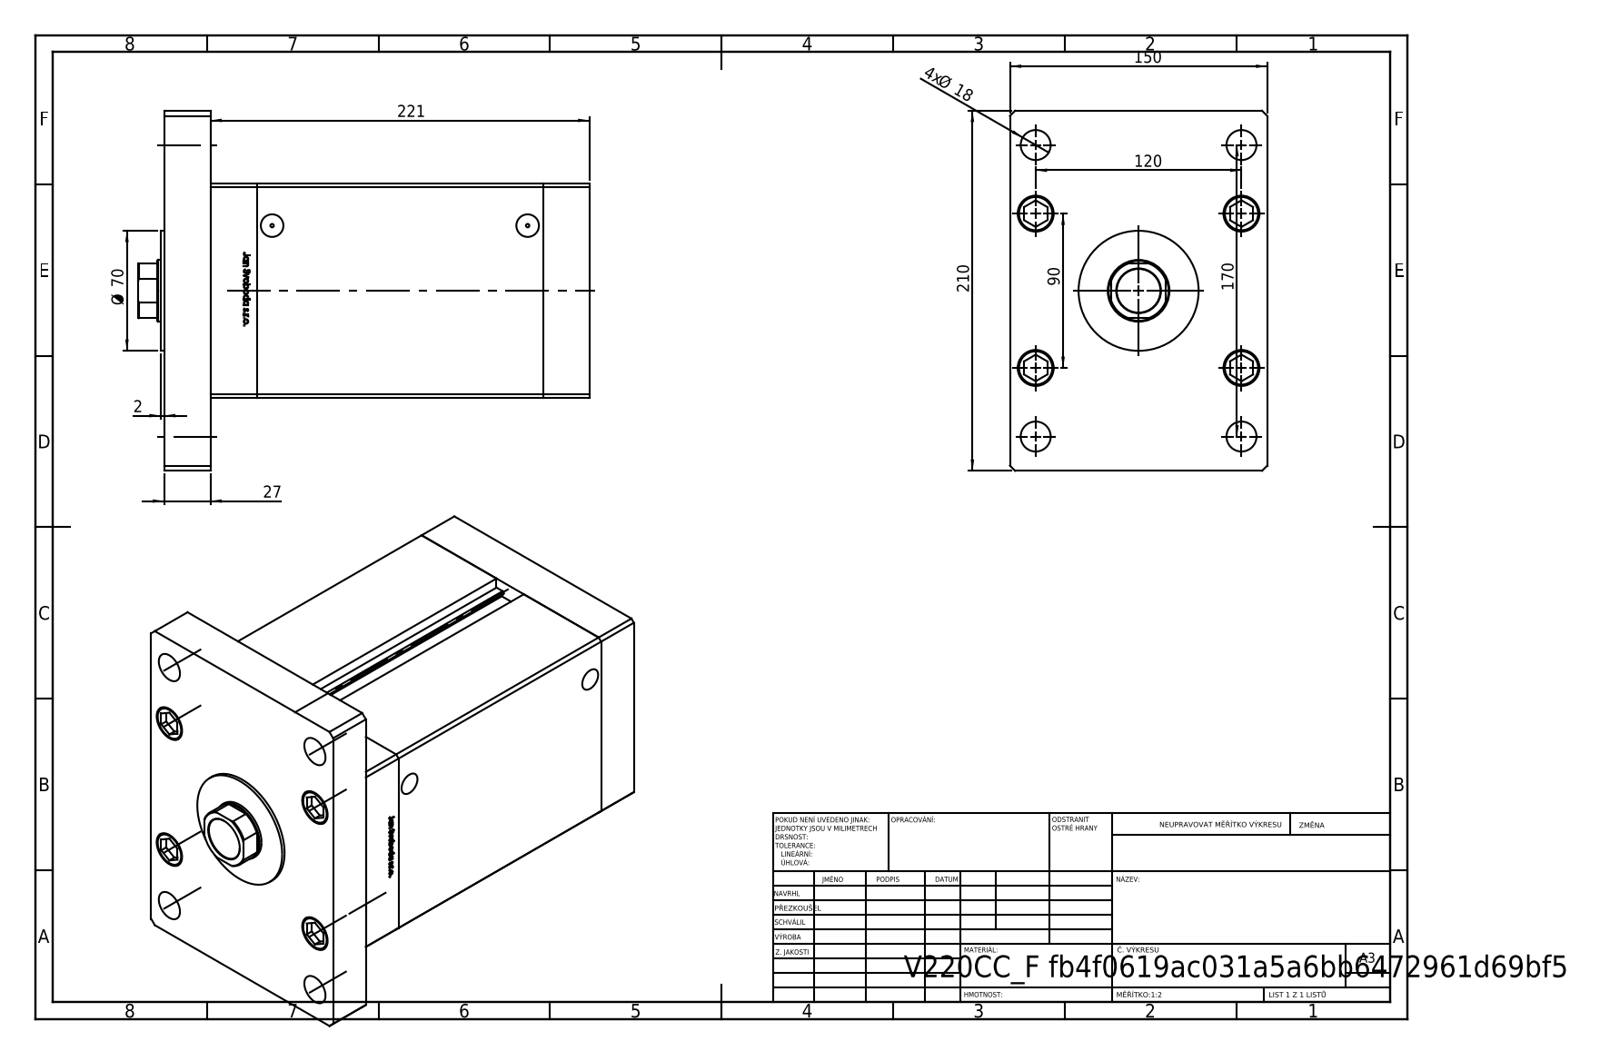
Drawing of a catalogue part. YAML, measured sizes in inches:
part_name: "ALLEN BOLT; V220C_FRONT_F; V220C_VC_F; V220C_F (+2 more)"
step_written_by: "SolidWorks 2019 (CONFIG_CONTROL_DESIGN)"
units: inches
bodies: {solids: 19, faces: 1308, planar: 515, cylindrical: 187, other: 606}
overall_size: [10.354, 8.268, 5.906]
volume: 266.2
surface_area: 731.9
round_holes:
  - {diameter: 0.689, count: 9}
  - {diameter: 0.866, count: 5}
  - {diameter: 0.63, count: 4}
  - {diameter: 0.827, count: 4}
  - {diameter: 0.079, count: 2}
  - {diameter: 0.518, count: 2}
  - {diameter: 1.004, count: 1}
  - {diameter: 1.417, count: 1}
  - {diameter: 1.476, count: 1}
round_bosses_or_shafts:
  - {diameter: 0.315, count: 9}
  - {diameter: 0.827, count: 5}
  - {diameter: 3.15, count: 1}
  - {diameter: 2.756, count: 1}
partial_cylinders:
  - {radius: 0.037, count: 2}
  - {radius: 0.689, count: 1}
face_to_face_distances: [1.063, 7.638, 8.701, 5.906, 4.921, 6.575, 2.126, 9.764, 1.319, 0.256]
hole_center_spacings: [2.008, 1.575, 2.953, 4.096, 4.724, 4.98, 5.118, 6.965]
